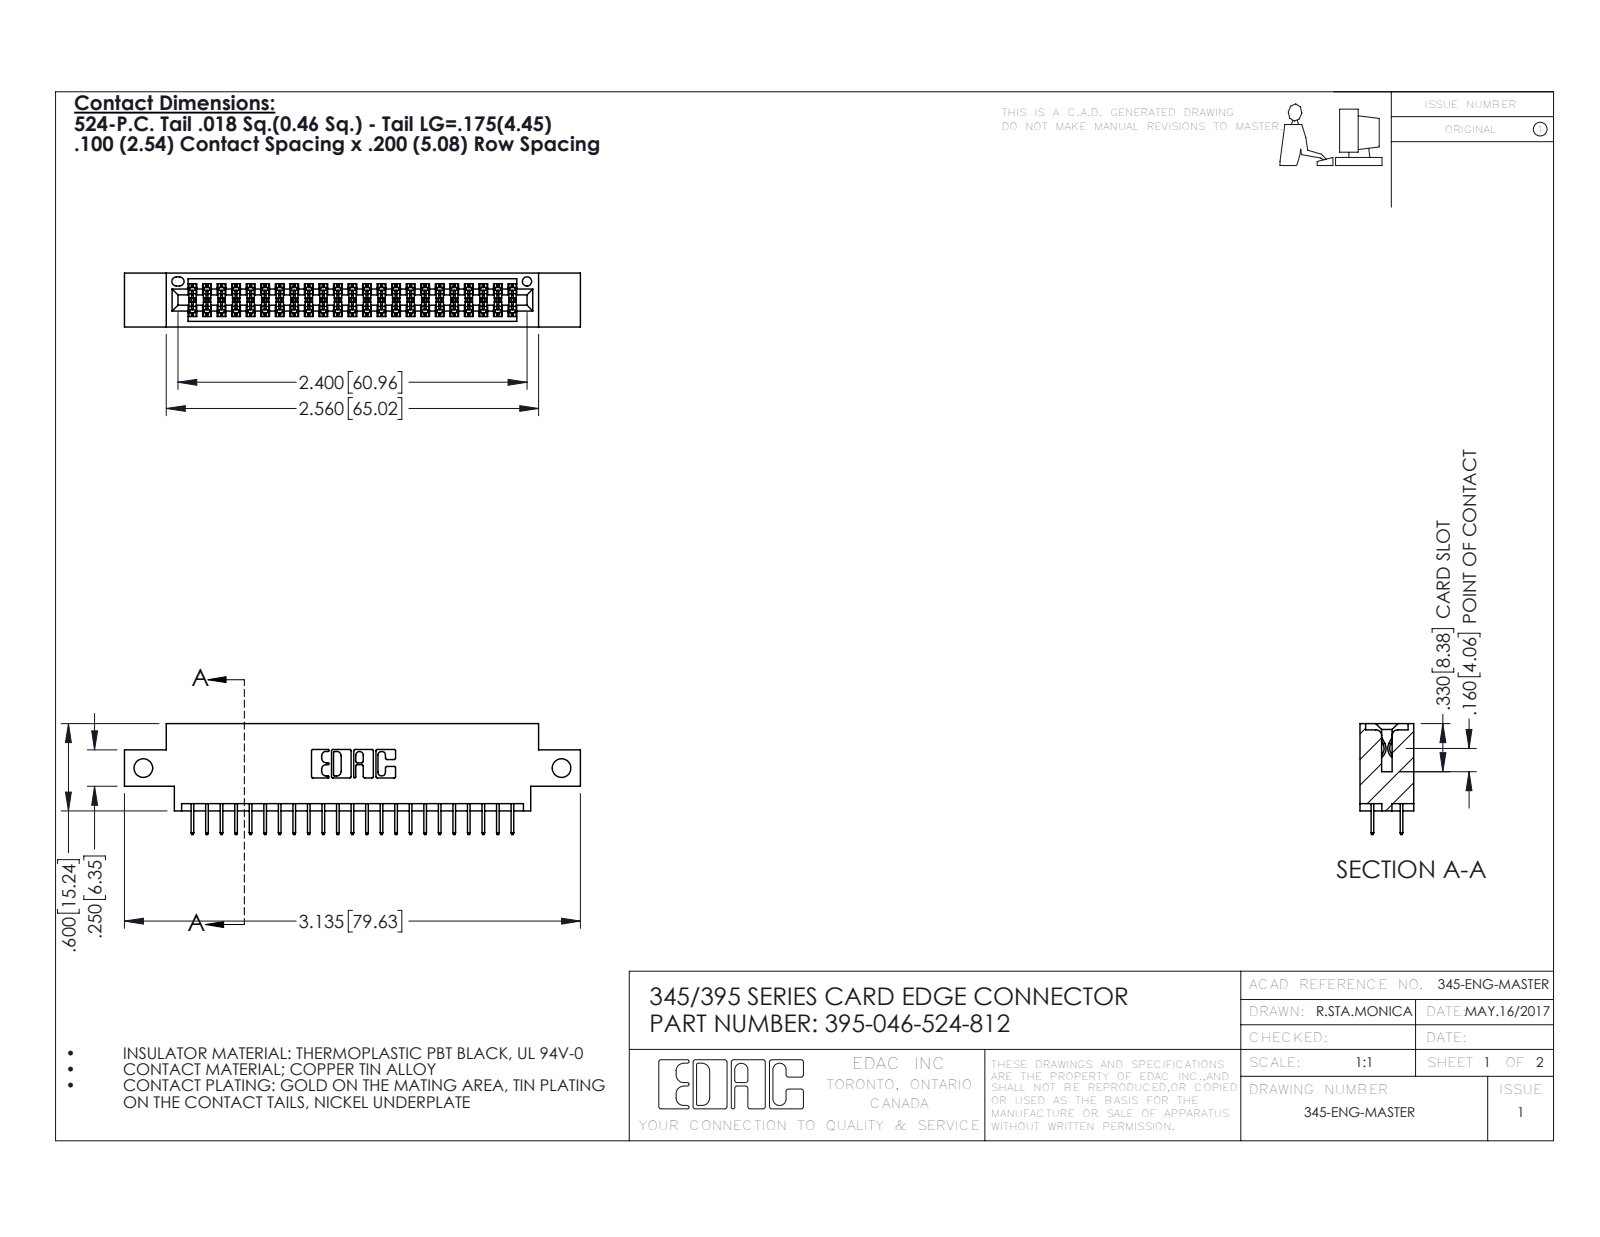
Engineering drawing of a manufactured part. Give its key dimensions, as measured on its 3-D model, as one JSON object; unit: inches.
{"part_name": "345-292-001_345-293-124; 395-046-524-812; 345 Part_0.170 Offset - Side Mount", "step_written_by": "SolidWorks 2016 (CONFIG_CONTROL_DESIGN)", "units": "inches", "bodies": {"solids": 47, "faces": 2614, "planar": 1878, "cylindrical": 736, "other": 0}, "overall_size": [3.135, 0.762, 0.37], "volume_in3": 0.445, "surface_area_in2": 15.86, "round_holes": [[0.128, 2], [0.064, 1]], "partial_cylinders_radius": [[0.006, 69], [0.01, 22], [0.007, 6], [0.031, 6], [0.026, 3], [0.014, 2], [0.019, 2], [0.022, 2]], "face_to_face_distances": [0.072, 0.298, 0.37, 0.2, 0.098, 0.272, 0.025, 0.225, 0.175, 0.072], "hole_center_spacings": [2.875]}
